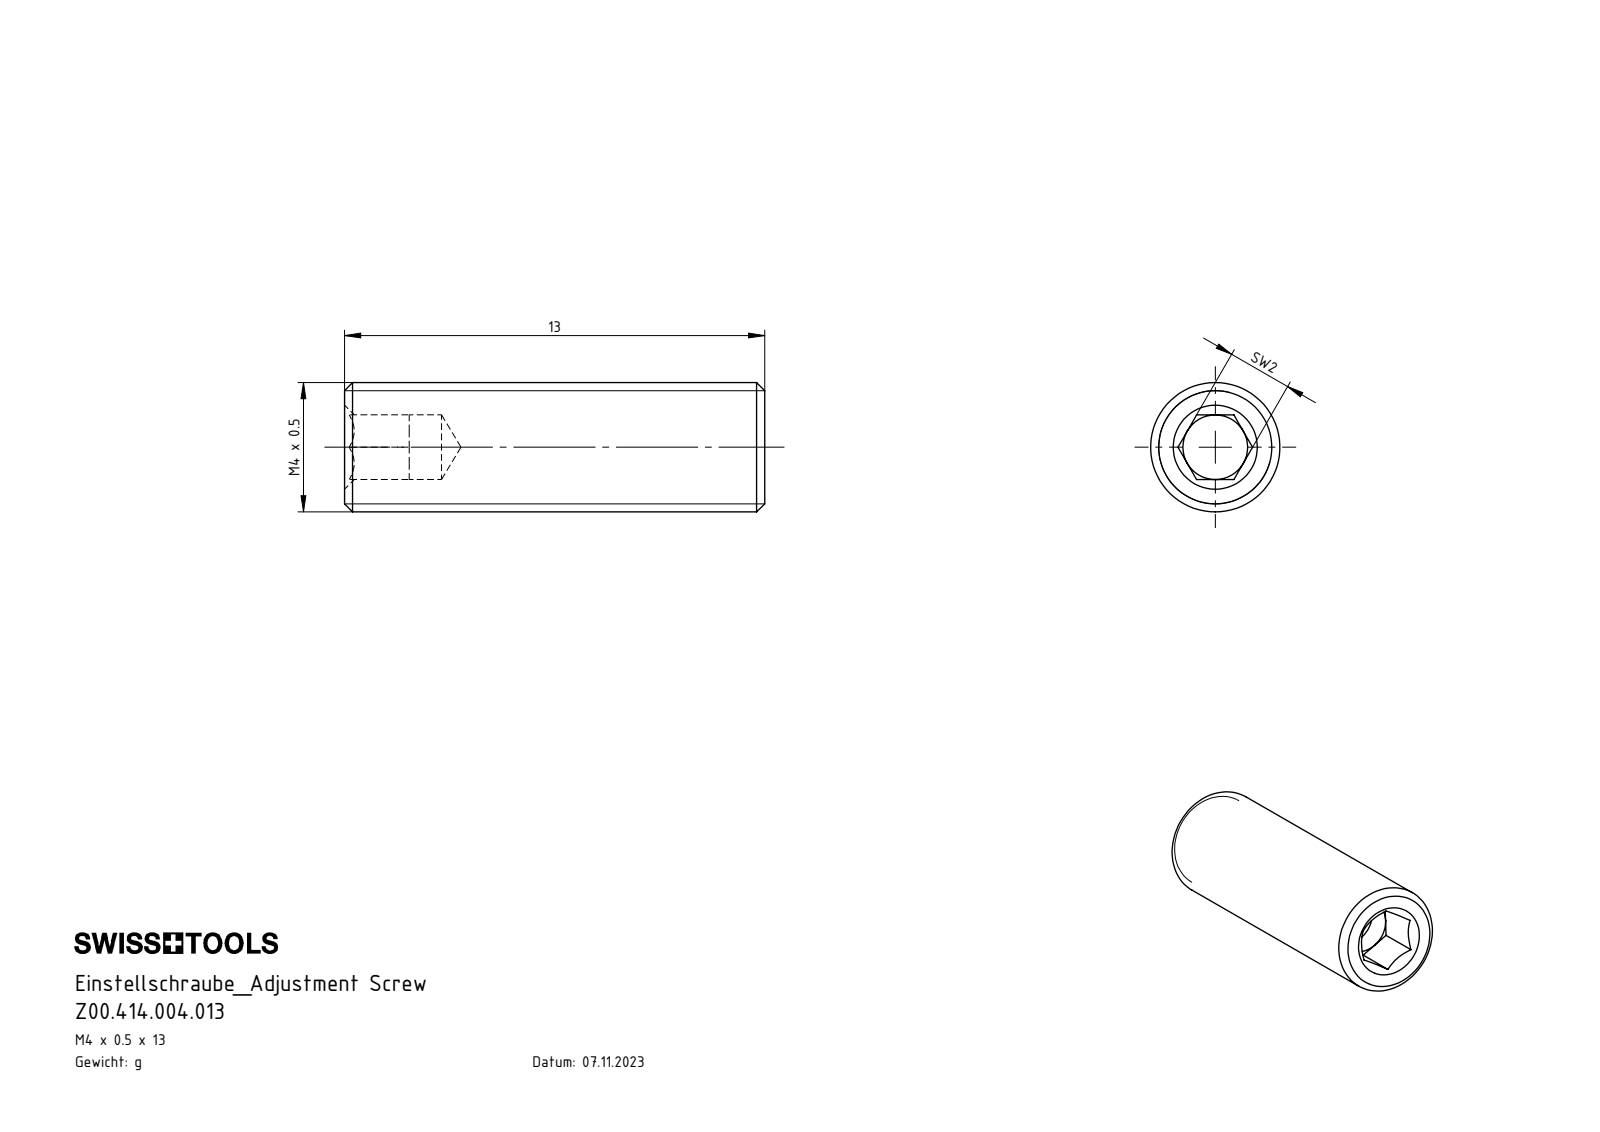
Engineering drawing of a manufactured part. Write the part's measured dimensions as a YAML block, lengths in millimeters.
part_name: "Z00.414.004.013"
step_written_by: "SolidWorks 2022 (AUTOMOTIVE_DESIGN)"
units: millimeters
bodies: {solids: 1, faces: 26, planar: 14, cylindrical: 4, other: 8}
overall_size: [13, 4, 4]
volume: 152
surface_area: 204
round_holes:
  - {diameter: 2, count: 1}
round_bosses_or_shafts:
  - {diameter: 4, count: 1}
face_to_face_distances: [2, 13, 11]
